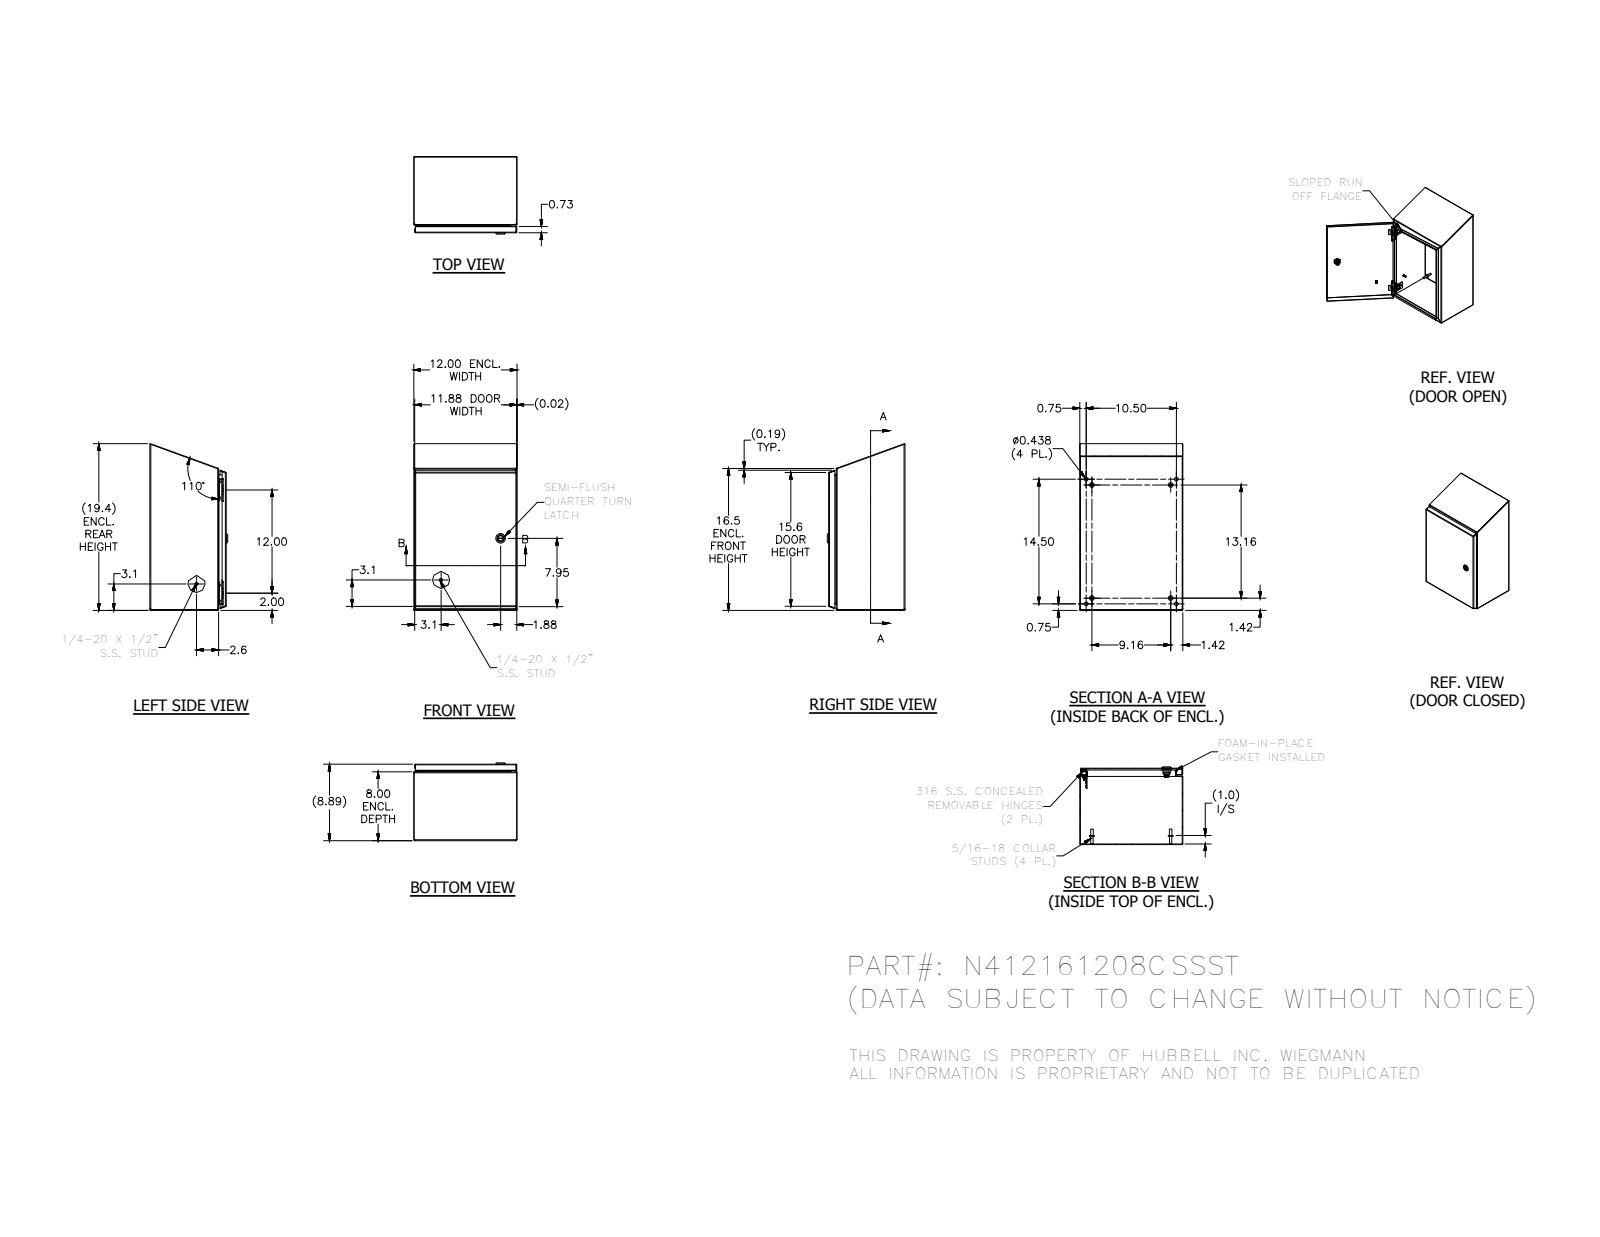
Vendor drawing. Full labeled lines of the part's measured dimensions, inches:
Part name (STEP PRODUCT): N412161208CSSST
STEP written by: SolidWorks 2018 (AUTOMOTIVE_DESIGN)
Units: inches
Bodies: 36 solids, 1426 faces (538 planar, 509 cylindrical, 379 other)
Overall size (bounding box): 19.391 × 12 × 9.044
Volume: 76.52 in³ · Surface area: 2 086 in²
Round holes (diameter × count): ⌀0.093 ×4, ⌀0.152 ×4, ⌀0.167 ×4, ⌀0.172 ×4, ⌀0.187 ×4, ⌀0.437 ×4, ⌀0.156 ×3, ⌀0.187 ×1, ⌀0.197 ×1, ⌀0.315 ×1, ⌀0.394 ×1, ⌀0.402 ×1
Round bosses / shafts (diameter × count): ⌀0.25 ×10, ⌀0.563 ×4, ⌀0.36 ×4, ⌀0.32 ×4, ⌀0.3 ×4, ⌀0.275 ×4, ⌀0.256 ×4, ⌀0.164 ×4
Partial cylindrical surfaces — rounded edges, fillets, slot ends (radius × count): R0.031 ×29, R0.05 ×26, R0.105 ×19, R0.016 ×18, R0.02 ×16, R0.125 ×16, R0.032 ×8, R0.524 ×6
Main face-to-face distances: 0.074, 8.813, 11.926, 8.739, 8.887, 12, 11.852, 7.926, 0.887, 0.813
Hole centre spacings: 12, 0.5, 0.656, 0.66, 0.952, 1.307, 1.311, 1.599
